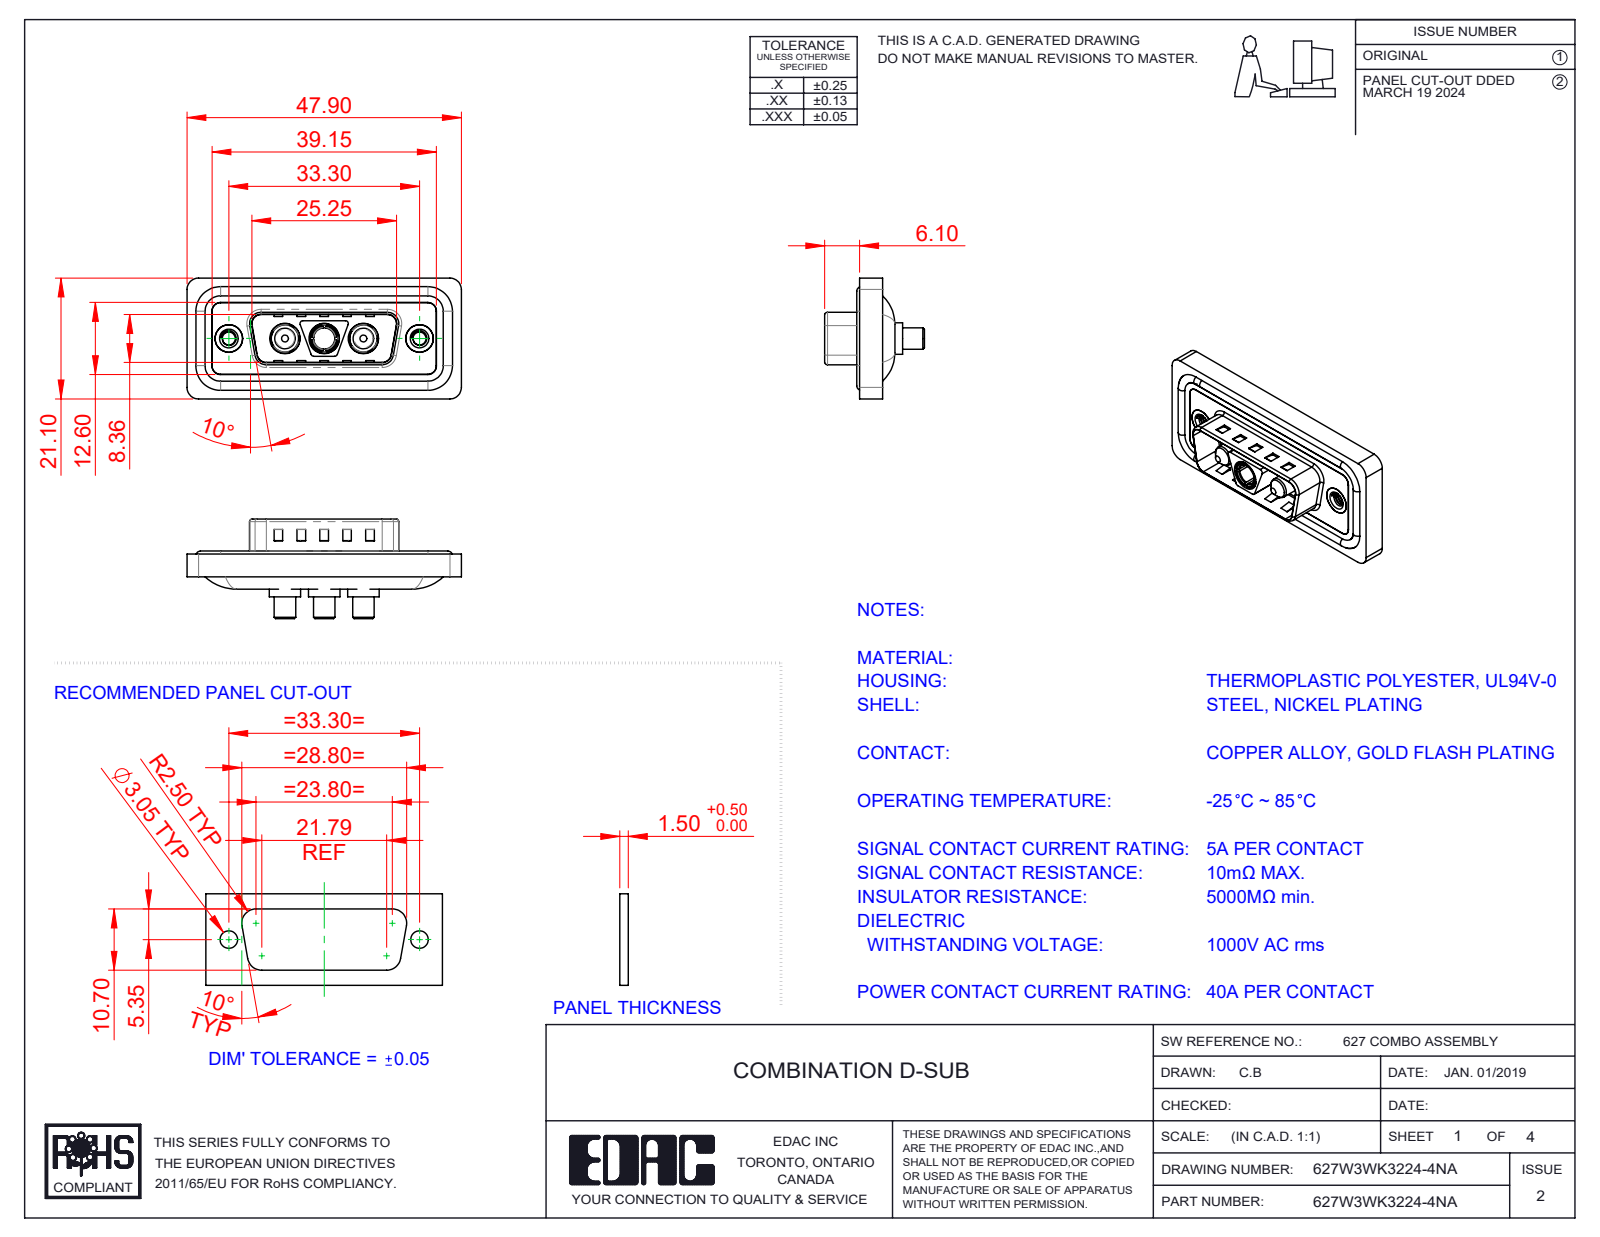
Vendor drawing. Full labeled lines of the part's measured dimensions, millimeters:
Part name (STEP PRODUCT): Power Socket_40A S; 627W3WK3224-4NA; 627Combo Waterproof Housing_15 Contacts; 627Combo Threaded Rivet_A (+4 more)
STEP written by: SolidWorks 2023 (CONFIG_CONTROL_DESIGN)
Units: millimetres
Bodies: 13 solids, 607 faces (231 planar, 252 cylindrical, 124 other)
Overall size (bounding box): 47.9 × 21.1 × 17.4
Volume: 5 745 mm³ · Surface area: 9 157 mm²
Round holes (diameter × count): ⌀4.85 ×3, ⌀5.3 ×3, ⌀2.26 ×2, ⌀4 ×2, ⌀4.8 ×2, ⌀5 ×2, ⌀3.7 ×1
Round bosses / shafts (diameter × count): ⌀1.6 ×4, ⌀5.5 ×3, ⌀5.2 ×3, ⌀4.75 ×3, ⌀3.75 ×3, ⌀4.9 ×2, ⌀3.6 ×2, ⌀4.96 ×1
Partial cylindrical surfaces — rounded edges, fillets, slot ends (radius × count): R1.5 ×26, R2 ×20, R0.5 ×12, R1.6 ×8, R0.25 ×4, R0.6 ×4, R0.65 ×4, R0.9 ×4
Main face-to-face distances: 0.4, 1.1, 0.5, 1.5, 1.6, 3.1, 2.9, 4, 0.82, 9.58
Hole centre spacings: 6.85, 9.8, 16.65, 23.5, 13.7, 33.3
